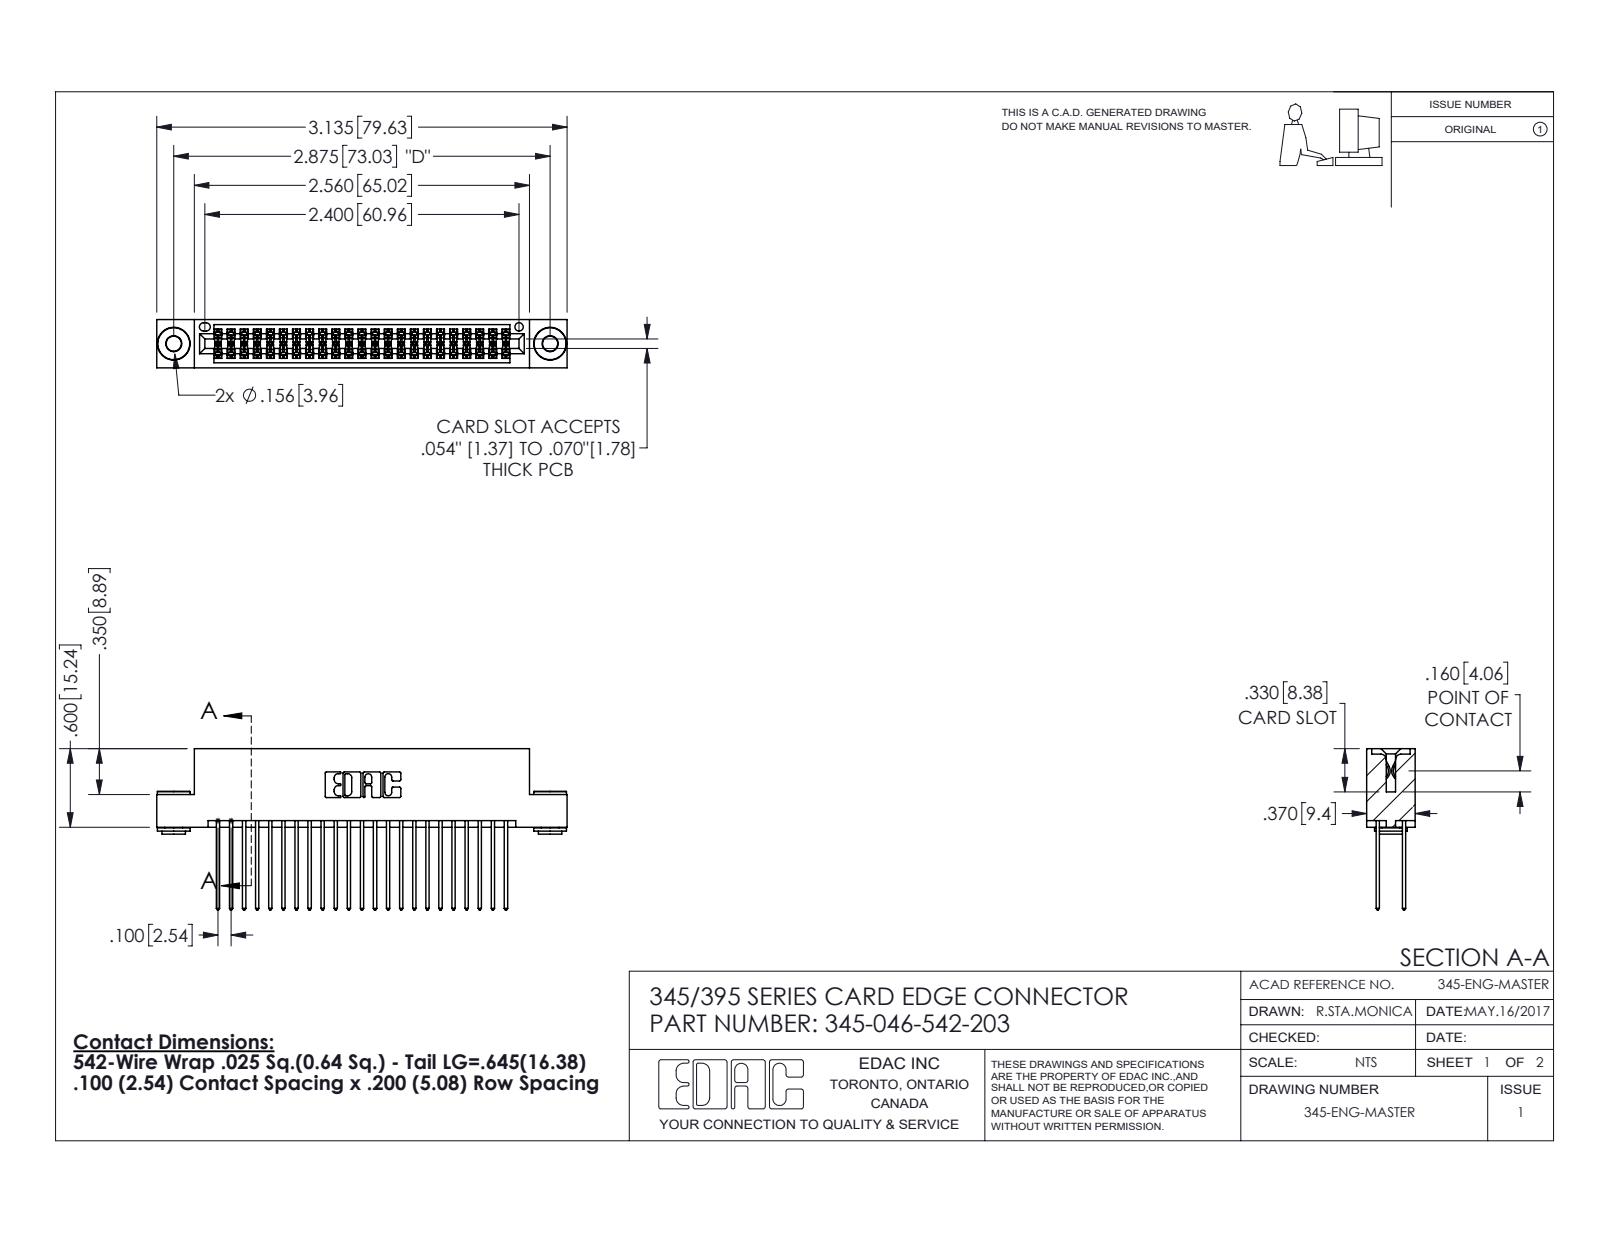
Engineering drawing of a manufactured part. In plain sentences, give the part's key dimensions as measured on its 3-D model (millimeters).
The part is named "345-292-001_345-293-142; 345 Part_Flush Mounting Lugs - 0.156 Dia-TH; 345-046-542-203; 345-250-002_345-250-002-102". Its 3-D file was written by "SolidWorks 2016 (CONFIG_CONTROL_DESIGN)". It is 49 solids with 2464 faces: 1608 planar, 848 cylindrical and 8 other. Overall it measures 79.6 by 31.3 by 9.4 millimeters. Its volume is 7 800 cubic millimeters and its surface area 12 350 square millimeters. Round holes: 2 of diameter 2.9, 2 of diameter 4, 1 of diameter 1.6. Round bosses or shafts: 2 of diameter 6.4, 2 of diameter 4.6, 2 of diameter 3.5. Partial cylindrical surfaces (rounded edges, fillets, slot ends): 69 of radius 0.2, 46 of radius 0.3, 22 of radius 0.3, 6 of radius 0.2, 6 of radius 0.8, 3 of radius 0.7, 2 of radius 0.4, 2 of radius 0.5. The main face-to-face distances are 1.8, 7.6, 5.1, 0.6, 2.5, 6.9, 9.4, 5.7, 4.4, 3.8. The hole center spacings are 6.9, 67.1, 73.
